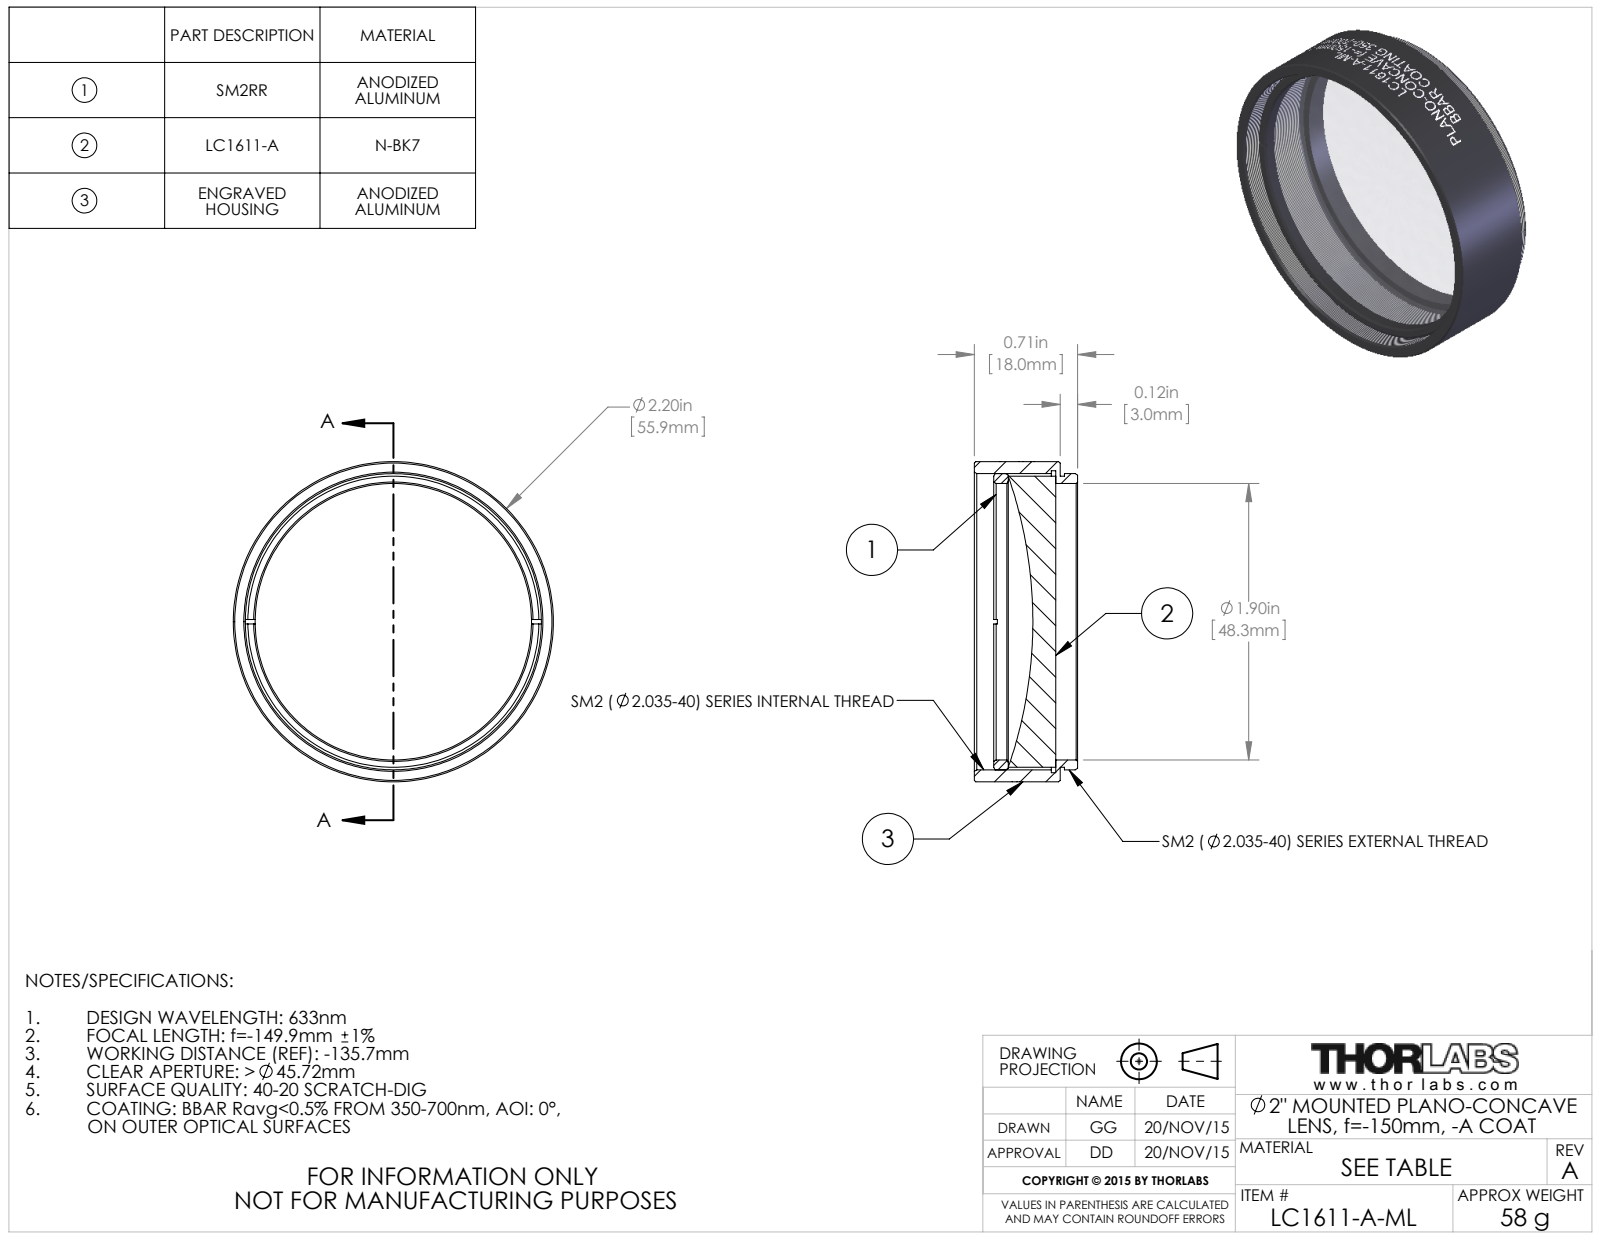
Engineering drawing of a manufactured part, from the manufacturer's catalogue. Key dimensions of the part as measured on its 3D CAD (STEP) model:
Part name (STEP PRODUCT): TTN045366-E0W
STEP written by: SolidWorks 2014 (CONFIG_CONTROL_DESIGN)
Units: inches
Bodies: 3 solids, 145 faces (16 planar, 107 cylindrical, 22 other)
Overall size (bounding box): 2.2 × 2.2 × 0.71
Volume: 1.175 in³ · Surface area: 21.85 in²
Round holes (diameter × count): ⌀1.9 ×1, ⌀2.075 ×1
Round bosses / shafts (diameter × count): ⌀2.2 ×1, ⌀2.035 ×1, ⌀2 ×1, ⌀1.999 ×1
Main face-to-face distances: 0.03, 0.59, 0.56, 0.12, 0.15, 0.71, 0.477, 0.357, 0.327, 0.233
